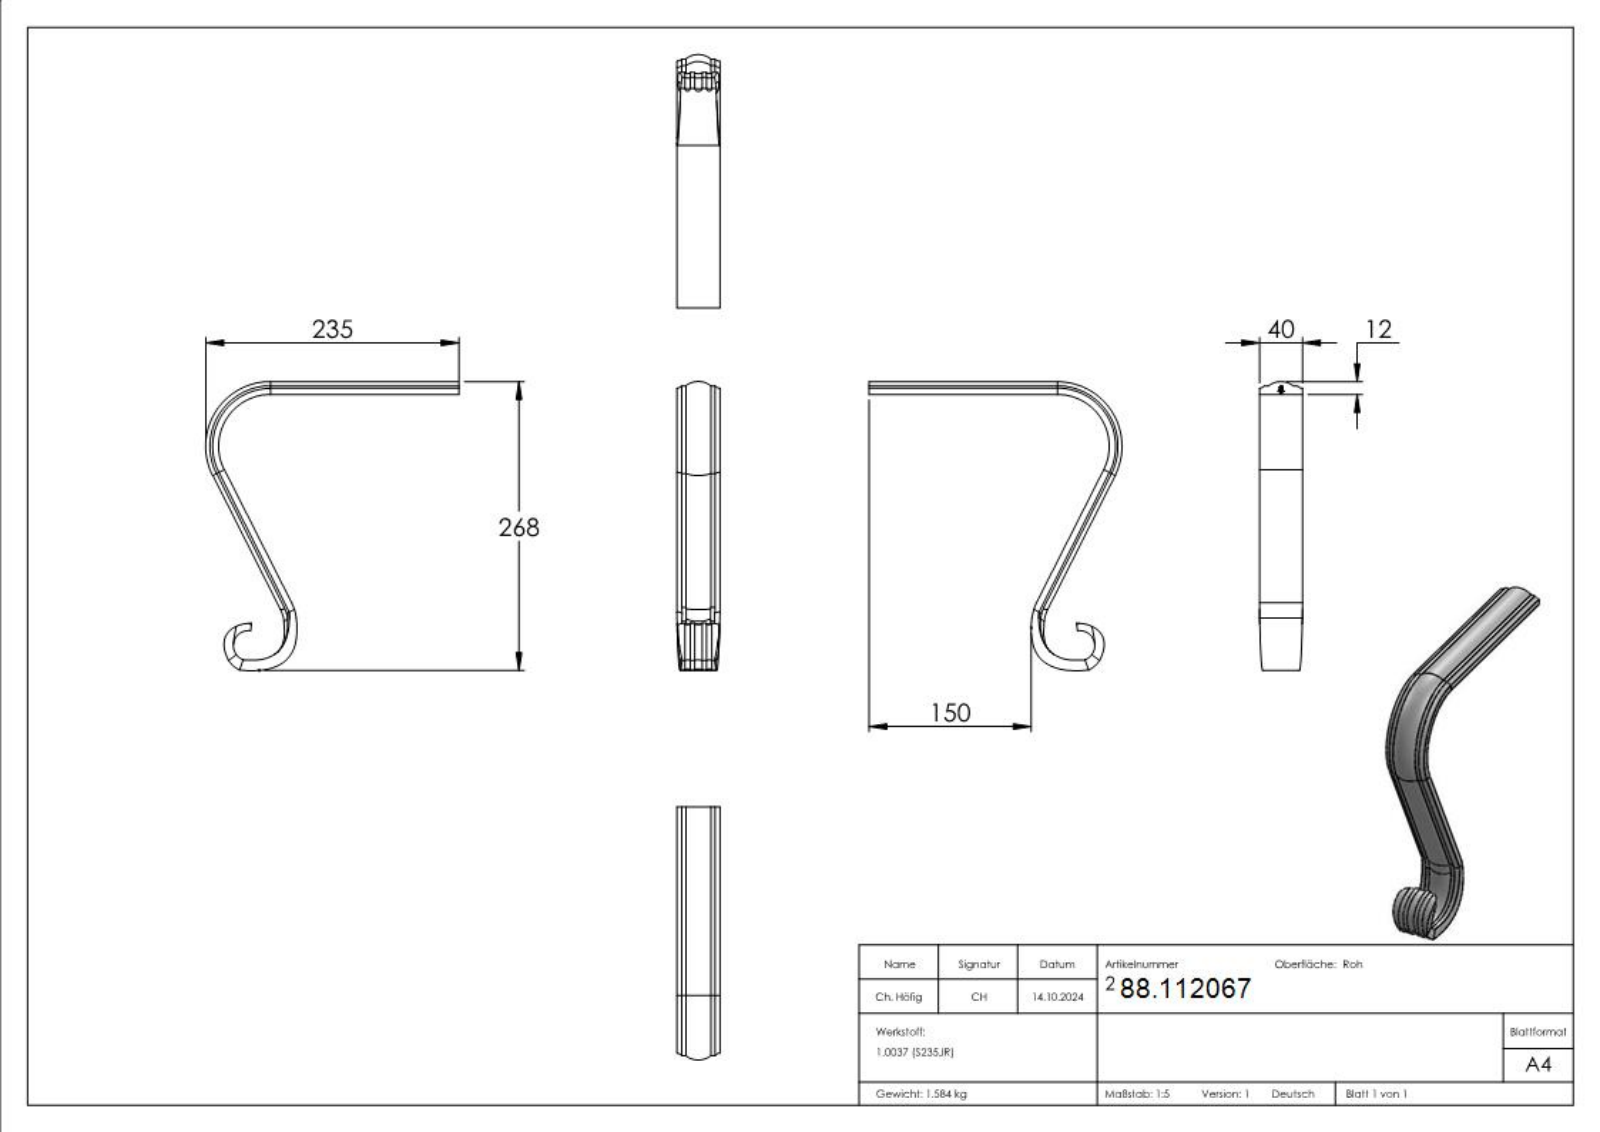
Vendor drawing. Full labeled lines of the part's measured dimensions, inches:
Part name (STEP PRODUCT): 2067
STEP written by: SolidWorks 2018 (CONFIG_CONTROL_DESIGN)
Units: inches
Bodies: 1 solid, 264 faces (123 planar, 9 cylindrical, 132 other)
Overall size (bounding box): 10.561 × 9.252 × 1.575
Volume: 12.39 in³ · Surface area: 82.76 in²
Partial cylindrical surfaces — rounded edges, fillets, slot ends (radius × count): R0.224 ×4, R0.73 ×2, R1.89 ×1, R2.205 ×1
Main face-to-face distances: 0.315, 1.575, 0.012, 0.016, 0.013, 0.017, 0.088, 0.123, 0.098, 0.081
